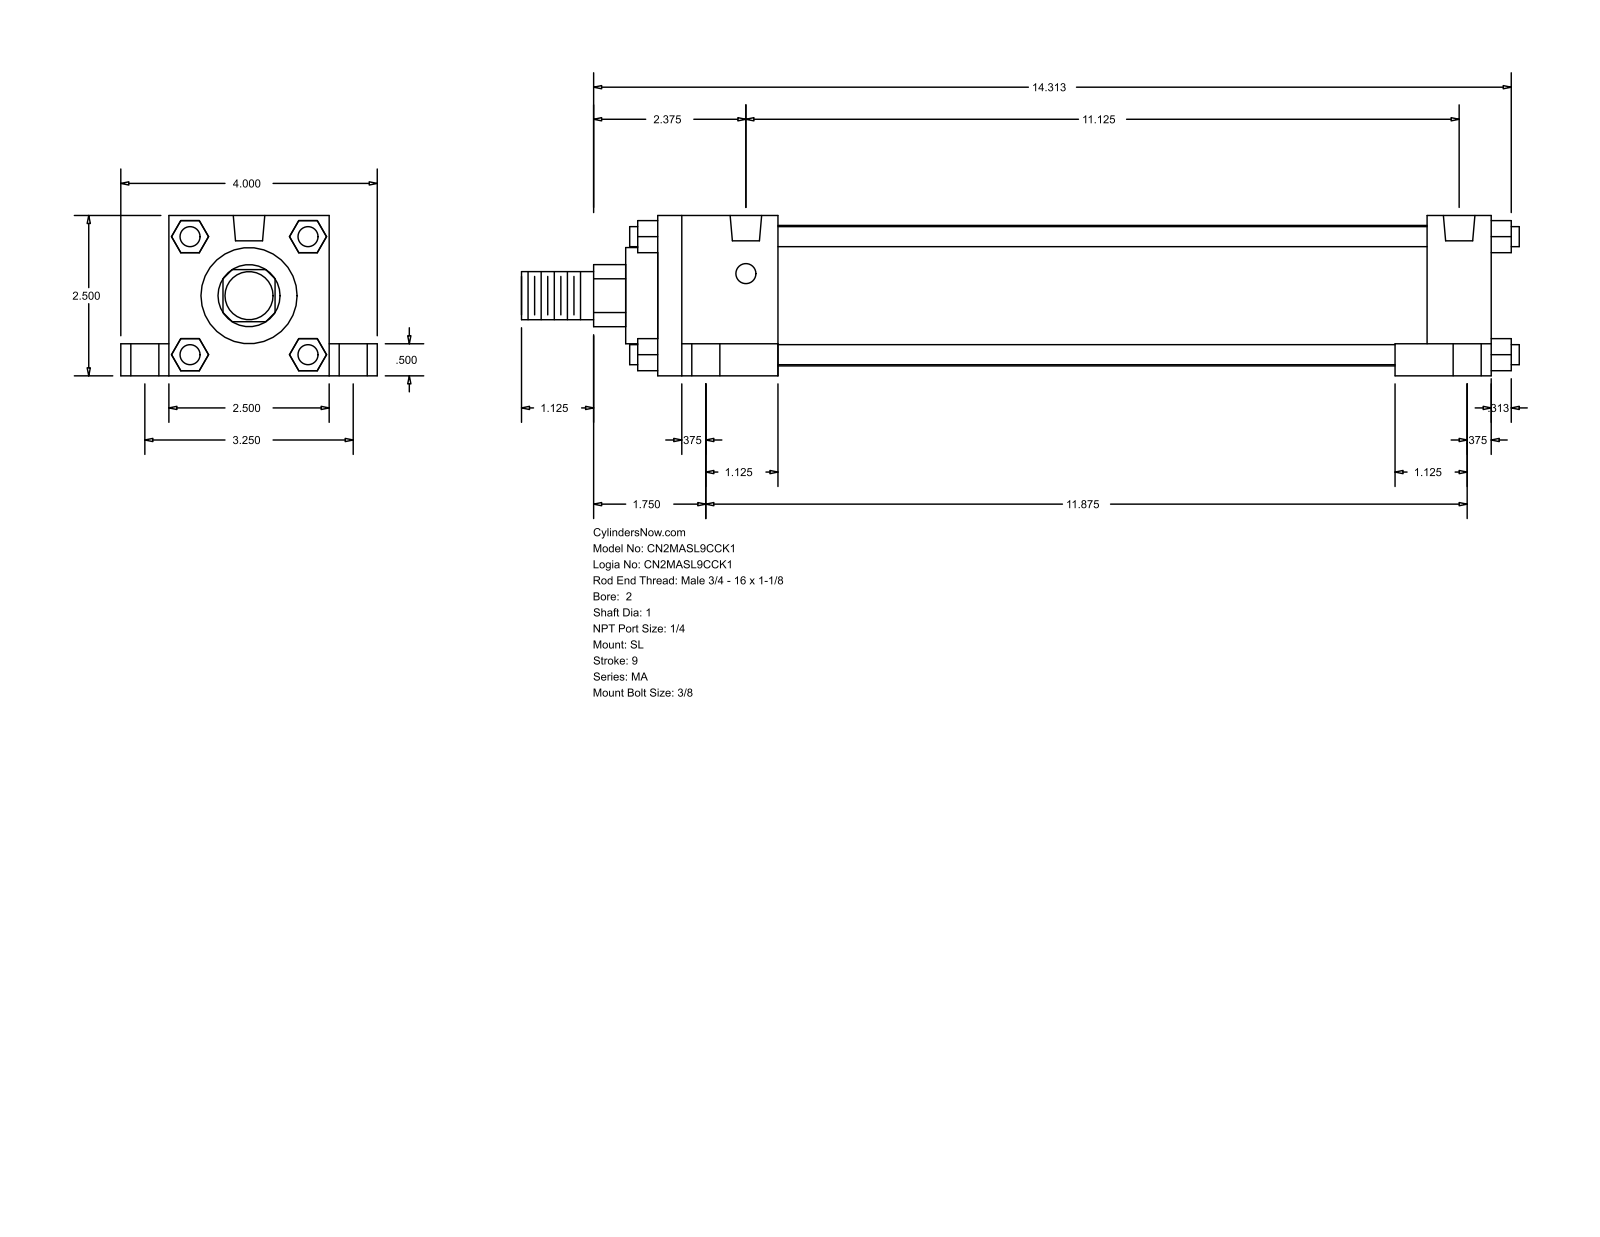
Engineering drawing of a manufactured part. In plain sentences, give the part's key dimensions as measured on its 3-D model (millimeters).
The part is named "MA_SL__0200_1". Its 3-D file was written by "GSSL Pune (CONFIG_CONTROL_DESIGN)". It is 0 solids with 148 faces: 112 planar, 36 cylindrical and 0 other. Overall it measures 395.29 by 101.6 by 63.5 millimeters. Round holes: 4 of diameter 7.94, 4 of diameter 11.11, 4 of diameter 17.46, 2 of diameter 12.49. Round bosses or shafts: 4 of diameter 7.94, 1 of diameter 55.63, 1 of diameter 38.1, 1 of diameter 25.4, 1 of diameter 19.05. Partial cylindrical surfaces (rounded edges, fillets, slot ends): 1 of radius 12.29. The main face-to-face distances are 63.5, 12.7, 330.2, 19.05, 82.55, 25.4, 50.8, 47.63, 282.57, 304.8. The hole center spacings are 41.39, 44.22, 82.54, 282.57, 288.7, 301.29, 301.62, 312.71.
